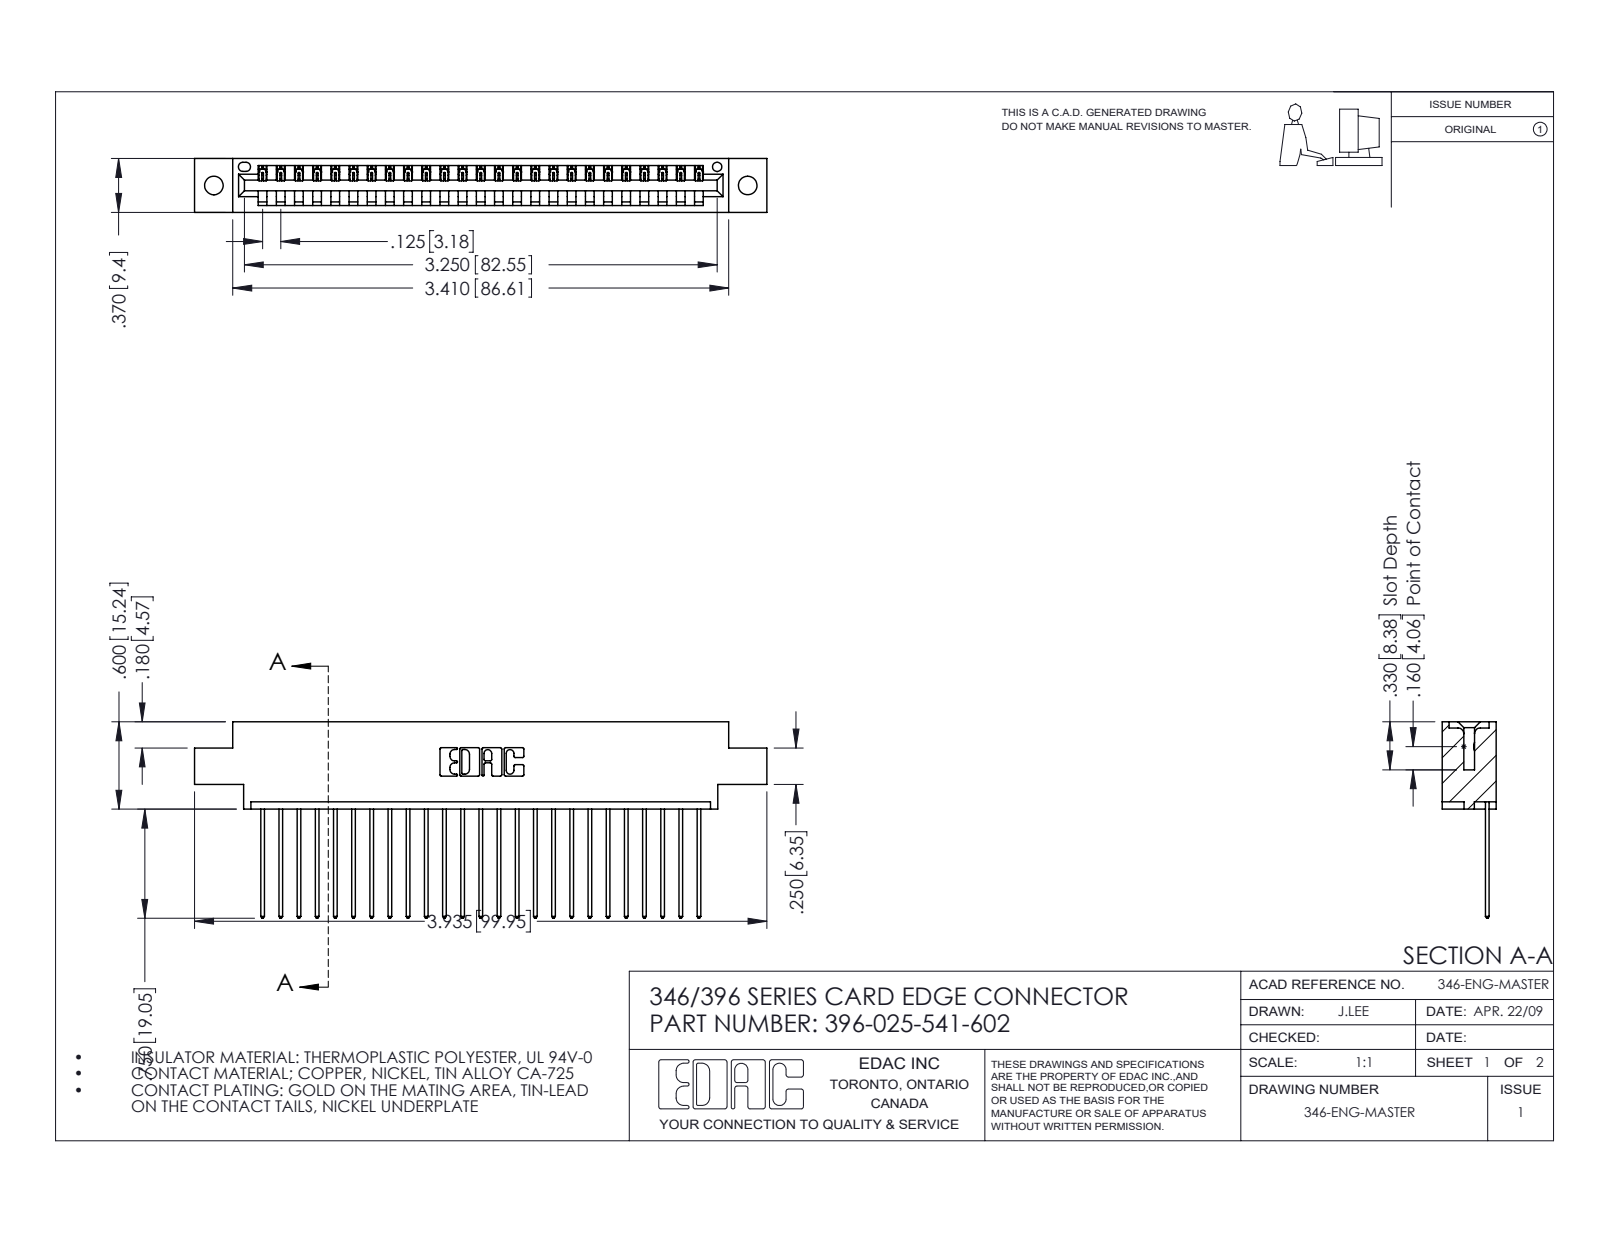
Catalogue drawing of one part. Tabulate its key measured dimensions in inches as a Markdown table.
| quantity | value |
| --- | --- |
| part name | 396-025-541-602; 346 Part_0.170 Offset - 0.128 Dia; 345-292-001_345-293-141 |
| STEP written by | SolidWorks 2016 (CONFIG_CONTROL_DESIGN) |
| units | inches |
| bodies | 26 solids, 1576 faces (1080 planar, 496 cylindrical, 0 other) |
| overall size | 3.935 × 1.35 × 0.37 |
| volume | 0.57 in³ |
| surface area | 18.4 in² |
| round holes (diameter × count) | 0.128 × 2, 0.064 × 1 |
| partial cylindrical surfaces (radius × count) | 0.006 × 50, 0.01 × 50, 0.01 × 22, 0.007 × 6, 0.031 × 6, 0.026 × 3, 0.031 × 2, 0.04 × 2 |
| main face-to-face distances | 0.048, 0.322, 0.37, 0.25, 0.072, 0.298, 0.025, 0.148, 0.222, 0.1 |
| hole center spacings | 0.246, 3.462, 3.67 |
